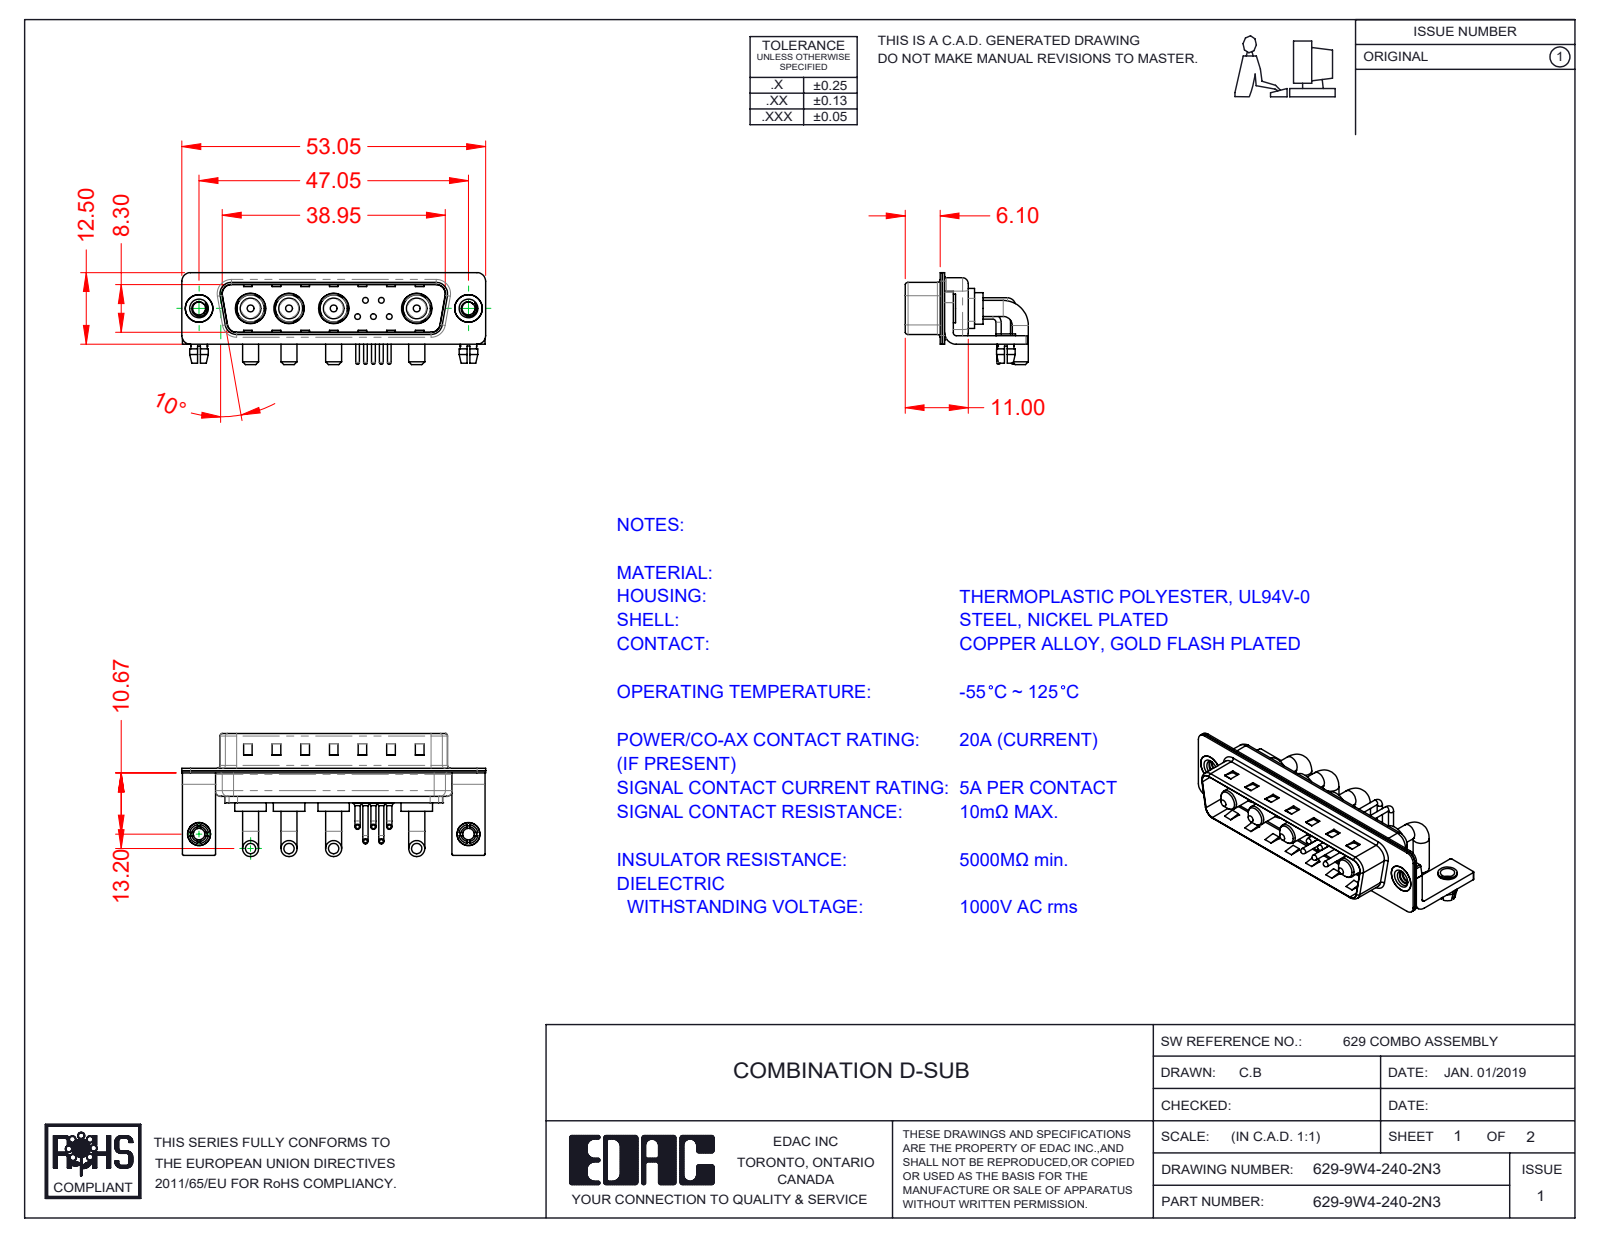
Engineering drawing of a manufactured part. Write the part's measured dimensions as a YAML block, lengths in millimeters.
part_name: "629Combo Stabilizer Bracket; 629Combo Housing_9W4; 629Combo Shell Rear_25 Contacts; 629-9W4-240-2N3 (+6 more)"
step_written_by: "SolidWorks 2020 (CONFIG_CONTROL_DESIGN)"
units: millimeters
bodies: {solids: 22, faces: 1230, planar: 599, cylindrical: 451, other: 180}
overall_size: [53.05, 21.5, 16.05]
volume: 3608
surface_area: 8048
round_holes:
  - {diameter: 2, count: 7}
  - {diameter: 0.75, count: 5}
  - {diameter: 1.6, count: 5}
  - {diameter: 4.85, count: 4}
  - {diameter: 5.3, count: 4}
  - {diameter: 2.26, count: 2}
  - {diameter: 2.5, count: 2}
  - {diameter: 3.2, count: 2}
  - {diameter: 4, count: 2}
  - {diameter: 4.8, count: 2}
round_bosses_or_shafts:
  - {diameter: 0.9, count: 10}
  - {diameter: 2.8, count: 8}
  - {diameter: 1.5, count: 5}
  - {diameter: 1, count: 5}
  - {diameter: 0.65, count: 5}
  - {diameter: 5.5, count: 4}
  - {diameter: 5.2, count: 4}
  - {diameter: 4.75, count: 4}
partial_cylinders:
  - {radius: 0.25, count: 16}
  - {radius: 1.5, count: 16}
  - {radius: 2, count: 13}
  - {radius: 0.5, count: 9}
  - {radius: 1.6, count: 8}
  - {radius: 1.01, count: 5}
  - {radius: 0.6, count: 4}
  - {radius: 0.65, count: 4}
face_to_face_distances: [0.4, 0.8, 9.5, 1.5, 9.1, 8.7, 9.9, 5.2, 0.75, 1.2]
hole_center_spacings: [3.16, 2.77, 5.04, 14.5, 47.05, 2.78, 4.4, 4.41]
